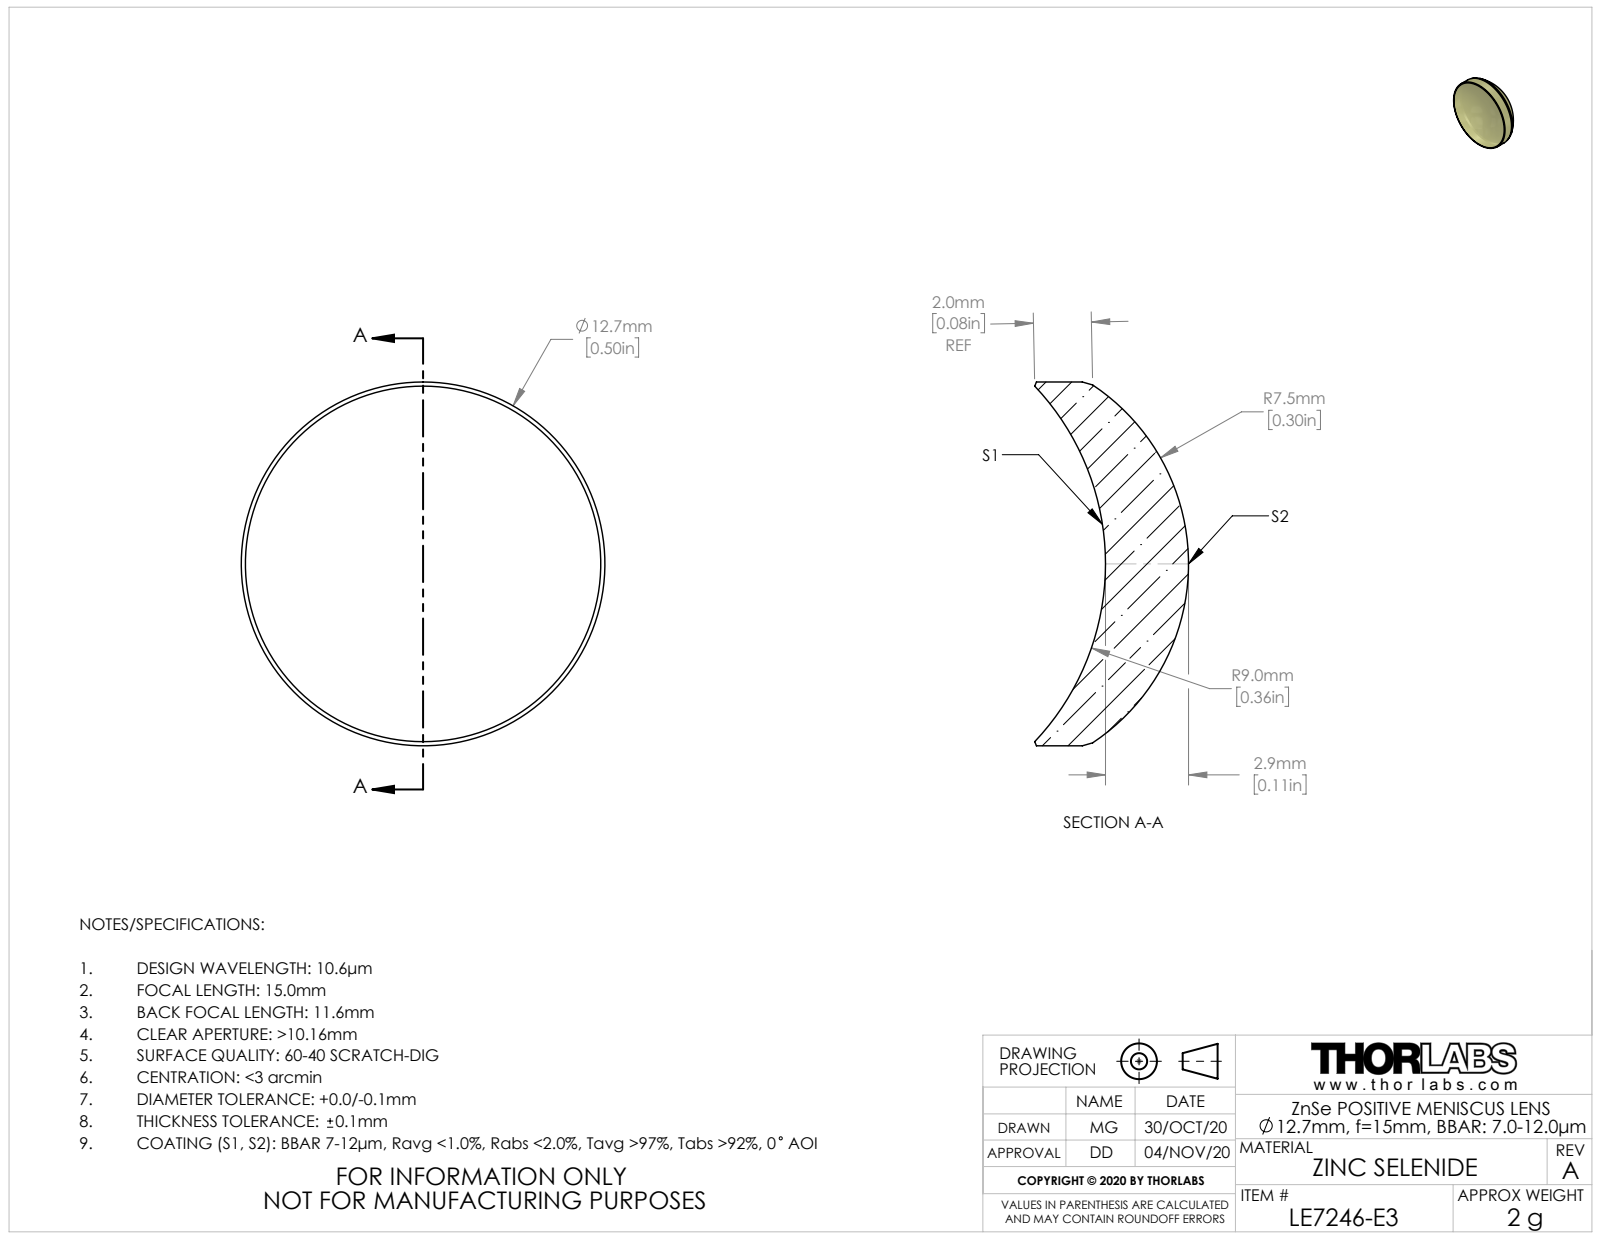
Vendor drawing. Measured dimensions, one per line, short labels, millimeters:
name: TTN225624-E0W
written by: SolidWorks 2018 (CONFIG_CONTROL_DESIGN)
unit: mm
bodies: 1 solid, 10 faces (0 planar, 2 cylindrical, 8 other)
size: 12.7 × 12.7 × 5.37
volume: 323 mm³; area: 383 mm²
bosses: 1× ⌀12.7
